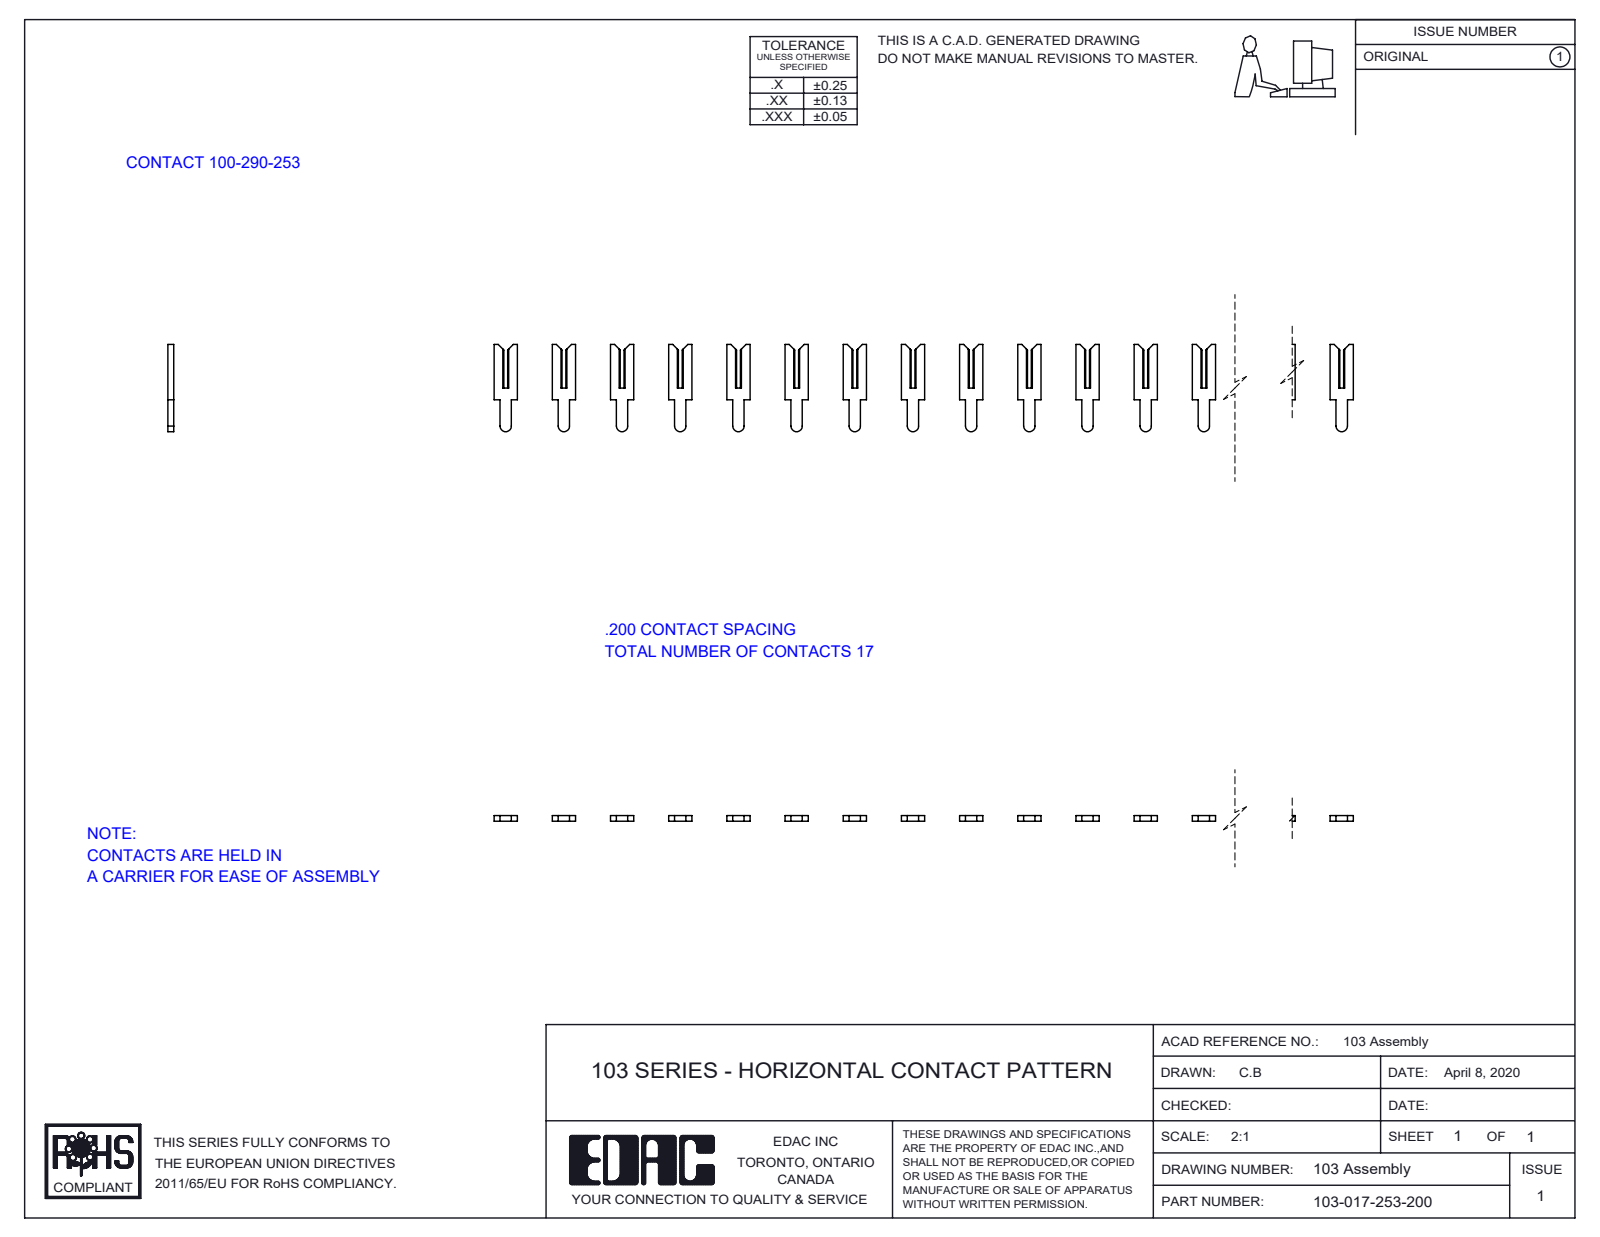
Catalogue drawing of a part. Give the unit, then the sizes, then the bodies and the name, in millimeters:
Units: millimetres
Overall size (bounding box): 83.3 × 7.6 × 0.5
Partial cylindrical surfaces — rounded edges, fillets, slot ends (radius × count): R0.5 ×17
Main face-to-face distances: 0.5, 5.1, 10.2, 15.2, 3.6, 20.3, 21.5, 7.2, 2, 25.4
Volume: 100 mm³ · Surface area: 585 mm²
Bodies: 17 solids, 340 faces (323 planar, 17 cylindrical, 0 other)
Part name (STEP PRODUCT): 100-290-001_100-290-253; 103-017-253-200
STEP written by: SolidWorks 2016 (CONFIG_CONTROL_DESIGN)
